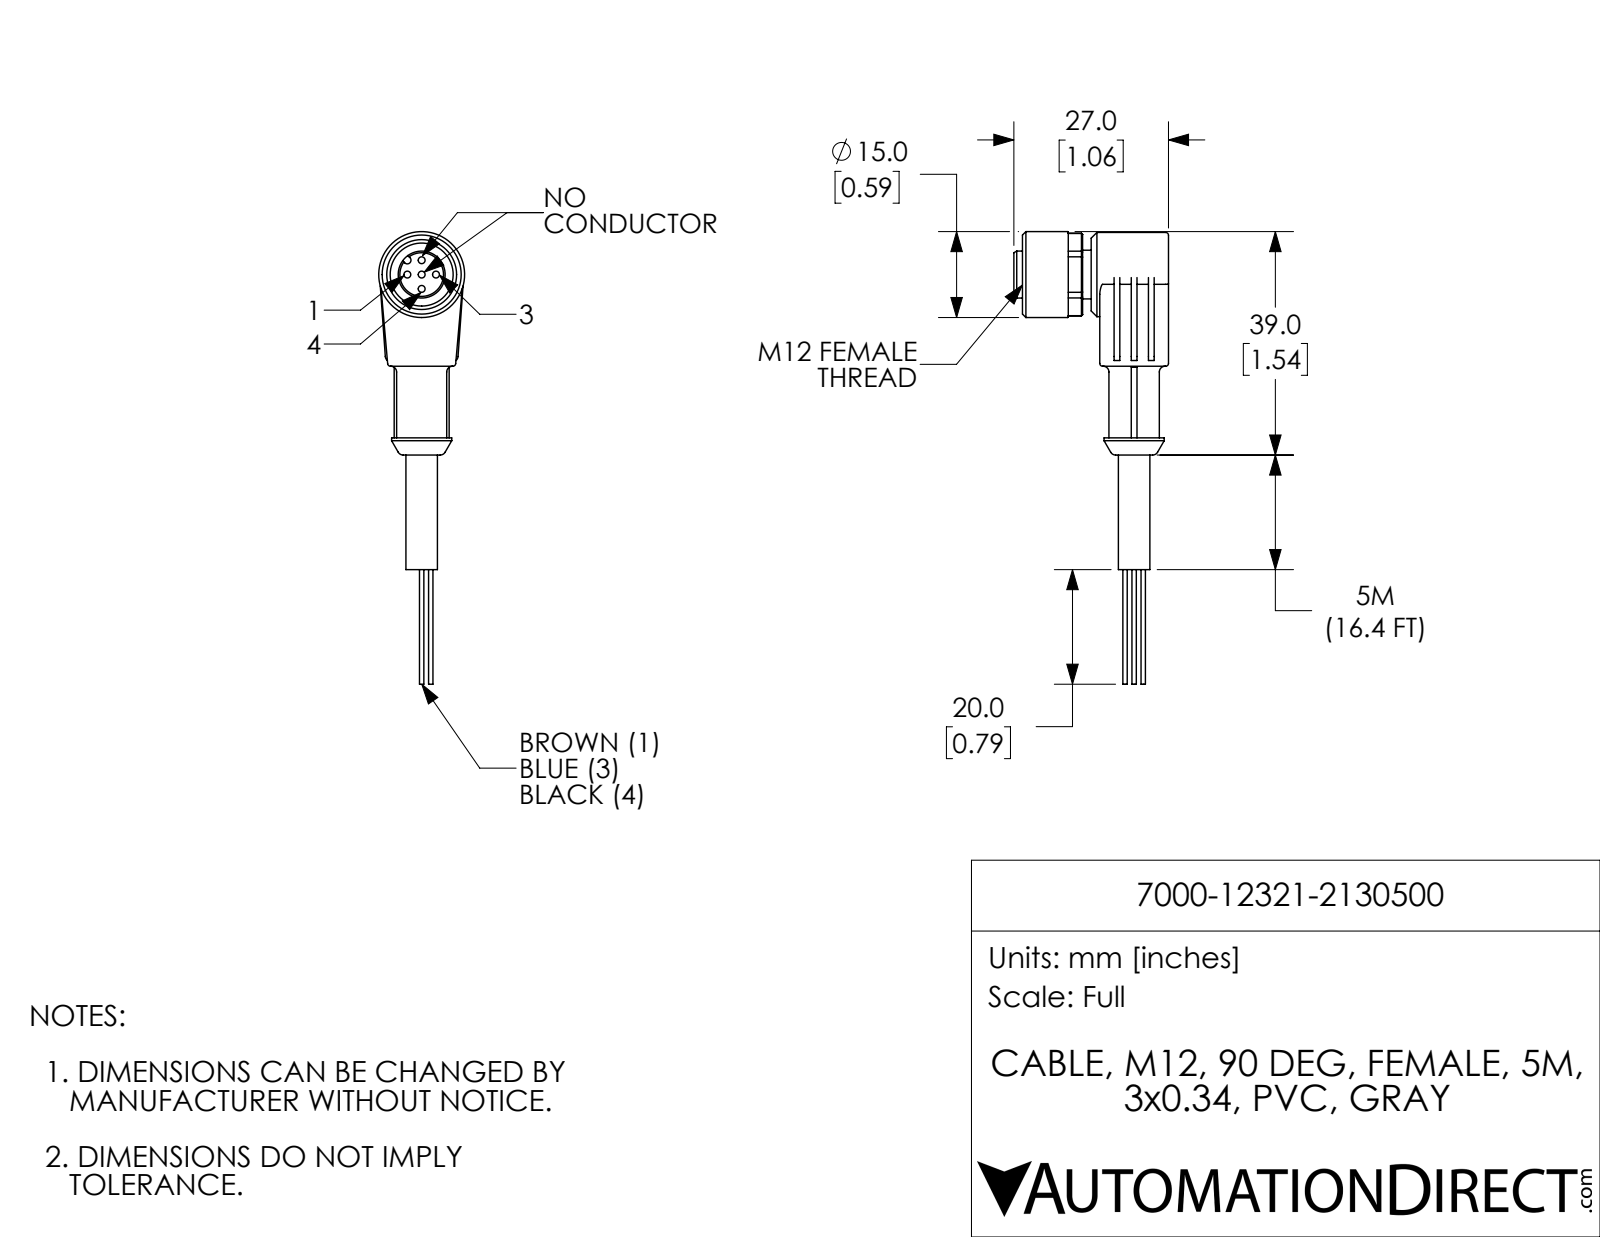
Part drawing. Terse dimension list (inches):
name: 7000-12321-2130500
written by: SolidWorks 2017 (AUTOMOTIVE_DESIGN)
unit: in
bodies: 1 solid, 149 faces (64 planar, 57 cylindrical, 28 other)
size: 3.11 × 1.063 × 0.591
volume: 0.417 in³; area: 5.822 in²
holes: 5× ⌀0.047, 1× ⌀0.189, 1× ⌀0.433
bosses: 3× ⌀0.03, 1× ⌀0.591, 1× ⌀0.579, 1× ⌀0.413, 1× ⌀0.346, 1× ⌀0.335, 1× ⌀0.323, 1× ⌀0.217
rounds: 8× R0.02, 2× R0.039, 1× R0.026, 1× R0.283
face distances: 0.472, 0.059, 0.118, 0.531, 0.591, 0.217, 0.374, 0.236, 0.315, 0.492
hole spacings: 0.098, 0.139, 0.197
